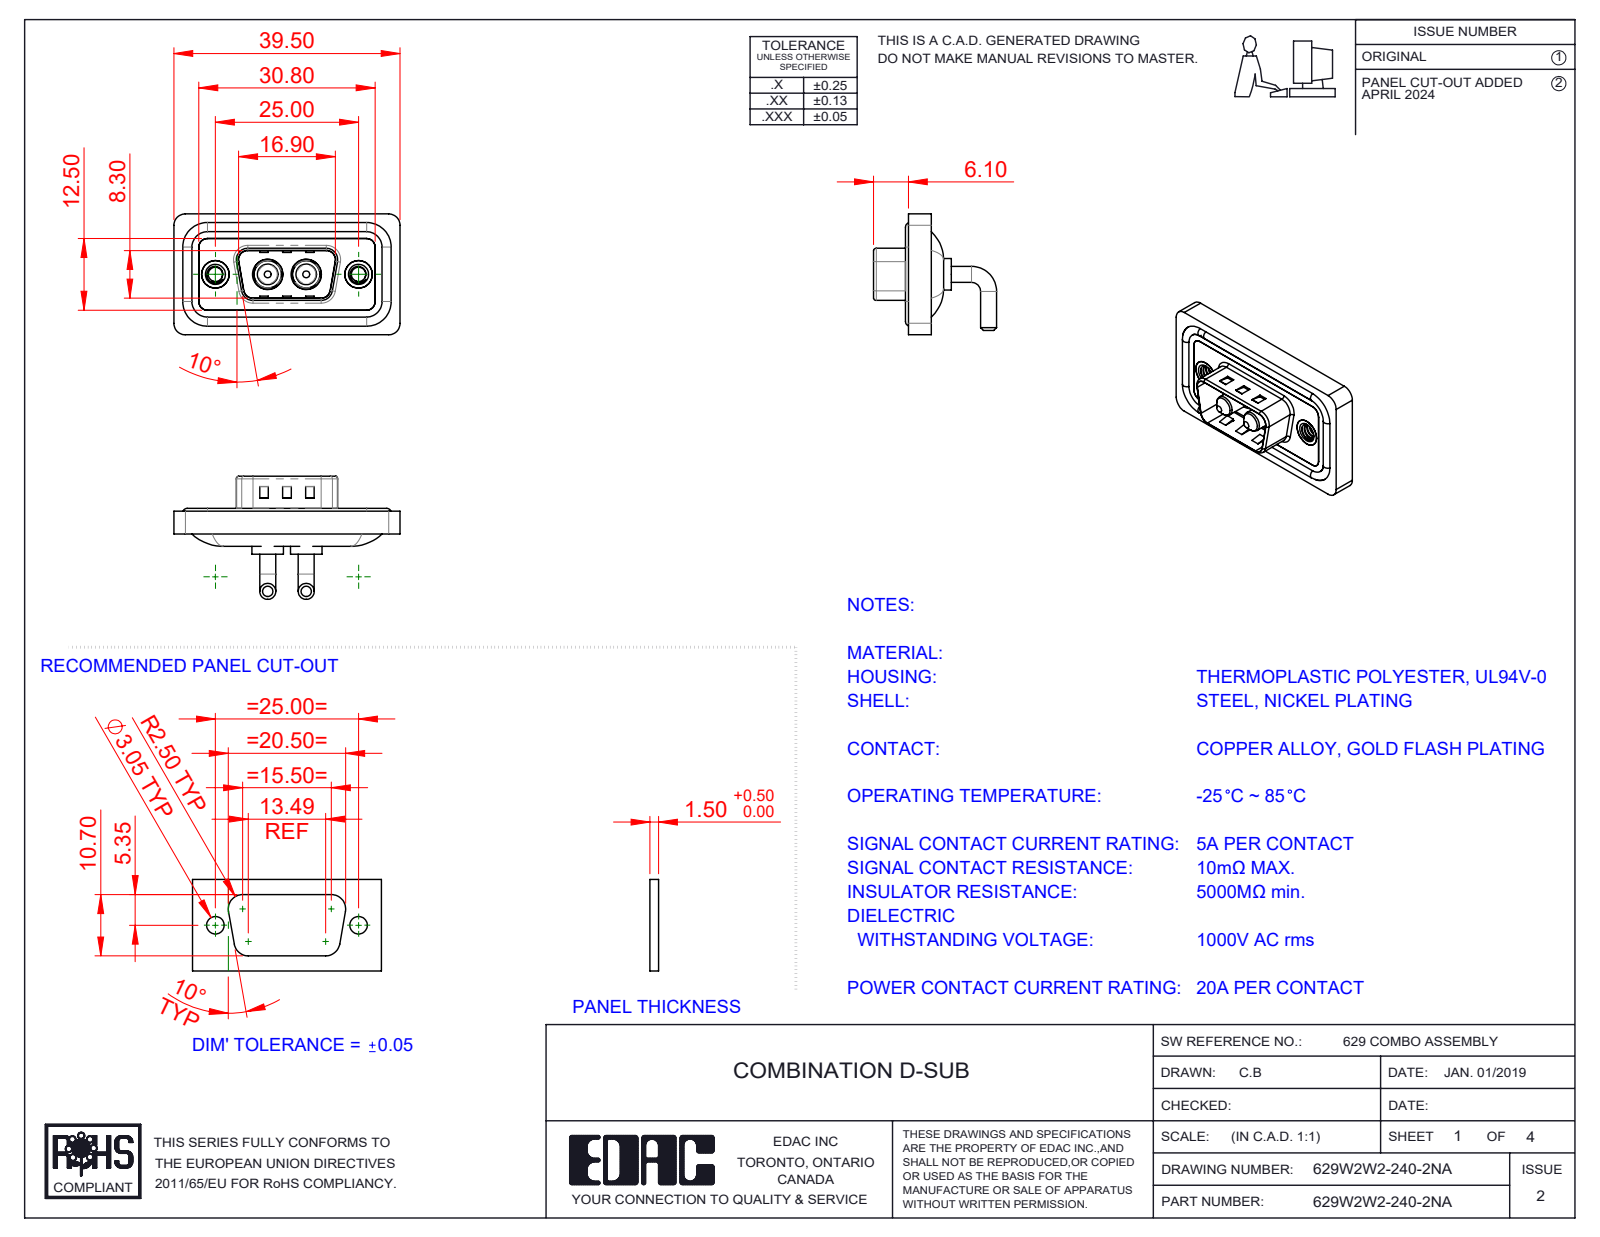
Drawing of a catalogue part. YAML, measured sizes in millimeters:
part_name: "629Combo Threaded Rivet_A; 629Combo Housing_2W2; Power Pin_20A RA; 629Combo Shell Front_09 Contacts (+3 more)"
step_written_by: "SolidWorks 2023 (CONFIG_CONTROL_DESIGN)"
units: millimeters
bodies: {solids: 11, faces: 491, planar: 165, cylindrical: 220, other: 106}
overall_size: [39.5, 21.5, 21.1]
volume: 4588
surface_area: 7171
round_holes:
  - {diameter: 2.5, count: 2}
  - {diameter: 4, count: 2}
  - {diameter: 4.8, count: 2}
  - {diameter: 4.85, count: 2}
  - {diameter: 5, count: 2}
  - {diameter: 5.3, count: 2}
round_bosses_or_shafts:
  - {diameter: 2.8, count: 4}
  - {diameter: 1.6, count: 4}
  - {diameter: 5.5, count: 2}
  - {diameter: 5.2, count: 2}
  - {diameter: 4.9, count: 2}
  - {diameter: 4.75, count: 2}
  - {diameter: 3.75, count: 2}
  - {diameter: 3.6, count: 2}
partial_cylinders:
  - {radius: 1.5, count: 18}
  - {radius: 2, count: 18}
  - {radius: 0.5, count: 8}
  - {radius: 1.6, count: 8}
  - {radius: 0.25, count: 4}
  - {radius: 0.6, count: 4}
  - {radius: 0.65, count: 4}
  - {radius: 0.9, count: 4}
face_to_face_distances: [0.4, 2.9, 1.1, 0.8, 2.1, 2.5, 3.1, 1.6, 4.5, 1.5]
hole_center_spacings: [9.14, 15.86, 6.72, 25]
